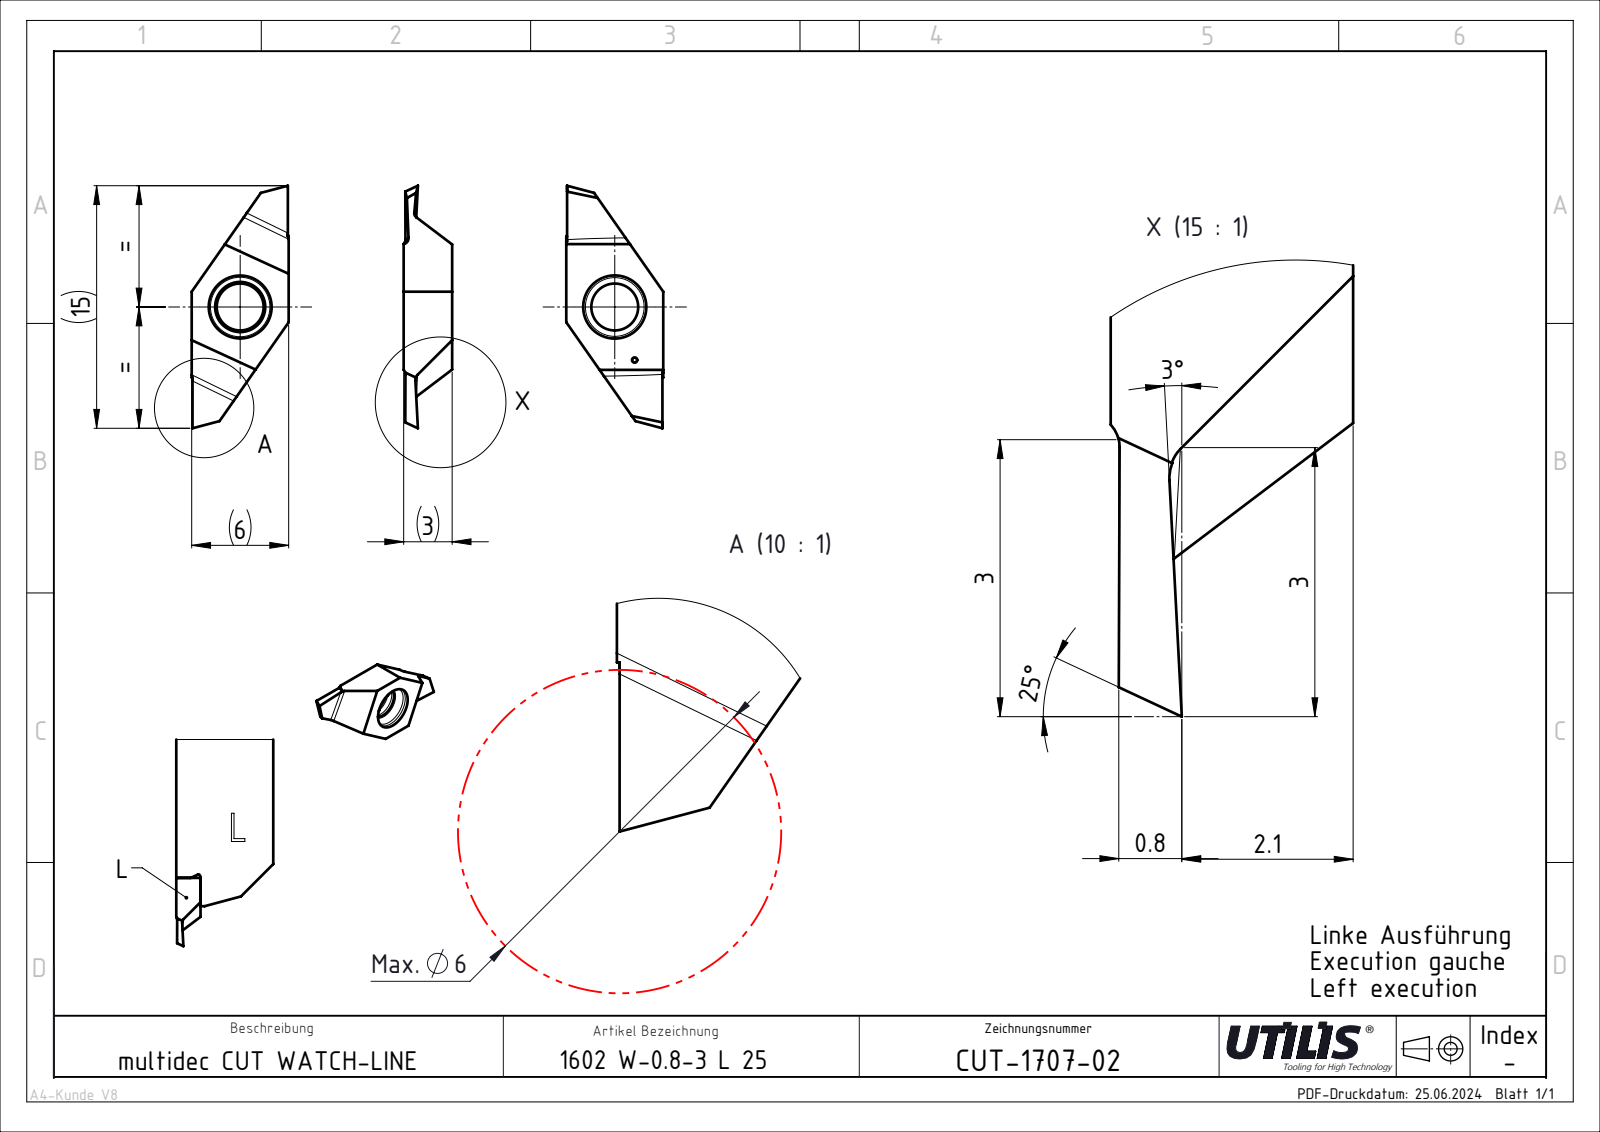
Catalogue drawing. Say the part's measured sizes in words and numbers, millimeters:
The part is named "CUT-1707; ASME Y14.5". Its 3-D file was written by "SolidWorks 2023 SP4 || FormatWorks Professional (AP242_MANAGED_MODEL_BASED_3D_ENGINEERING_MIM_LF)". It is 1 solid with 20 faces: 14 planar, 6 cylindrical and 0 other. Overall it measures 15 by 6 by 3 millimeters. Its volume is 101 cubic millimeters and its surface area 198 square millimeters. Round holes: 1 of diameter 2.9. Partial cylindrical surfaces (rounded edges, fillets, slot ends): 4 of radius 0.4. The main face-to-face distances are 6, 3.
